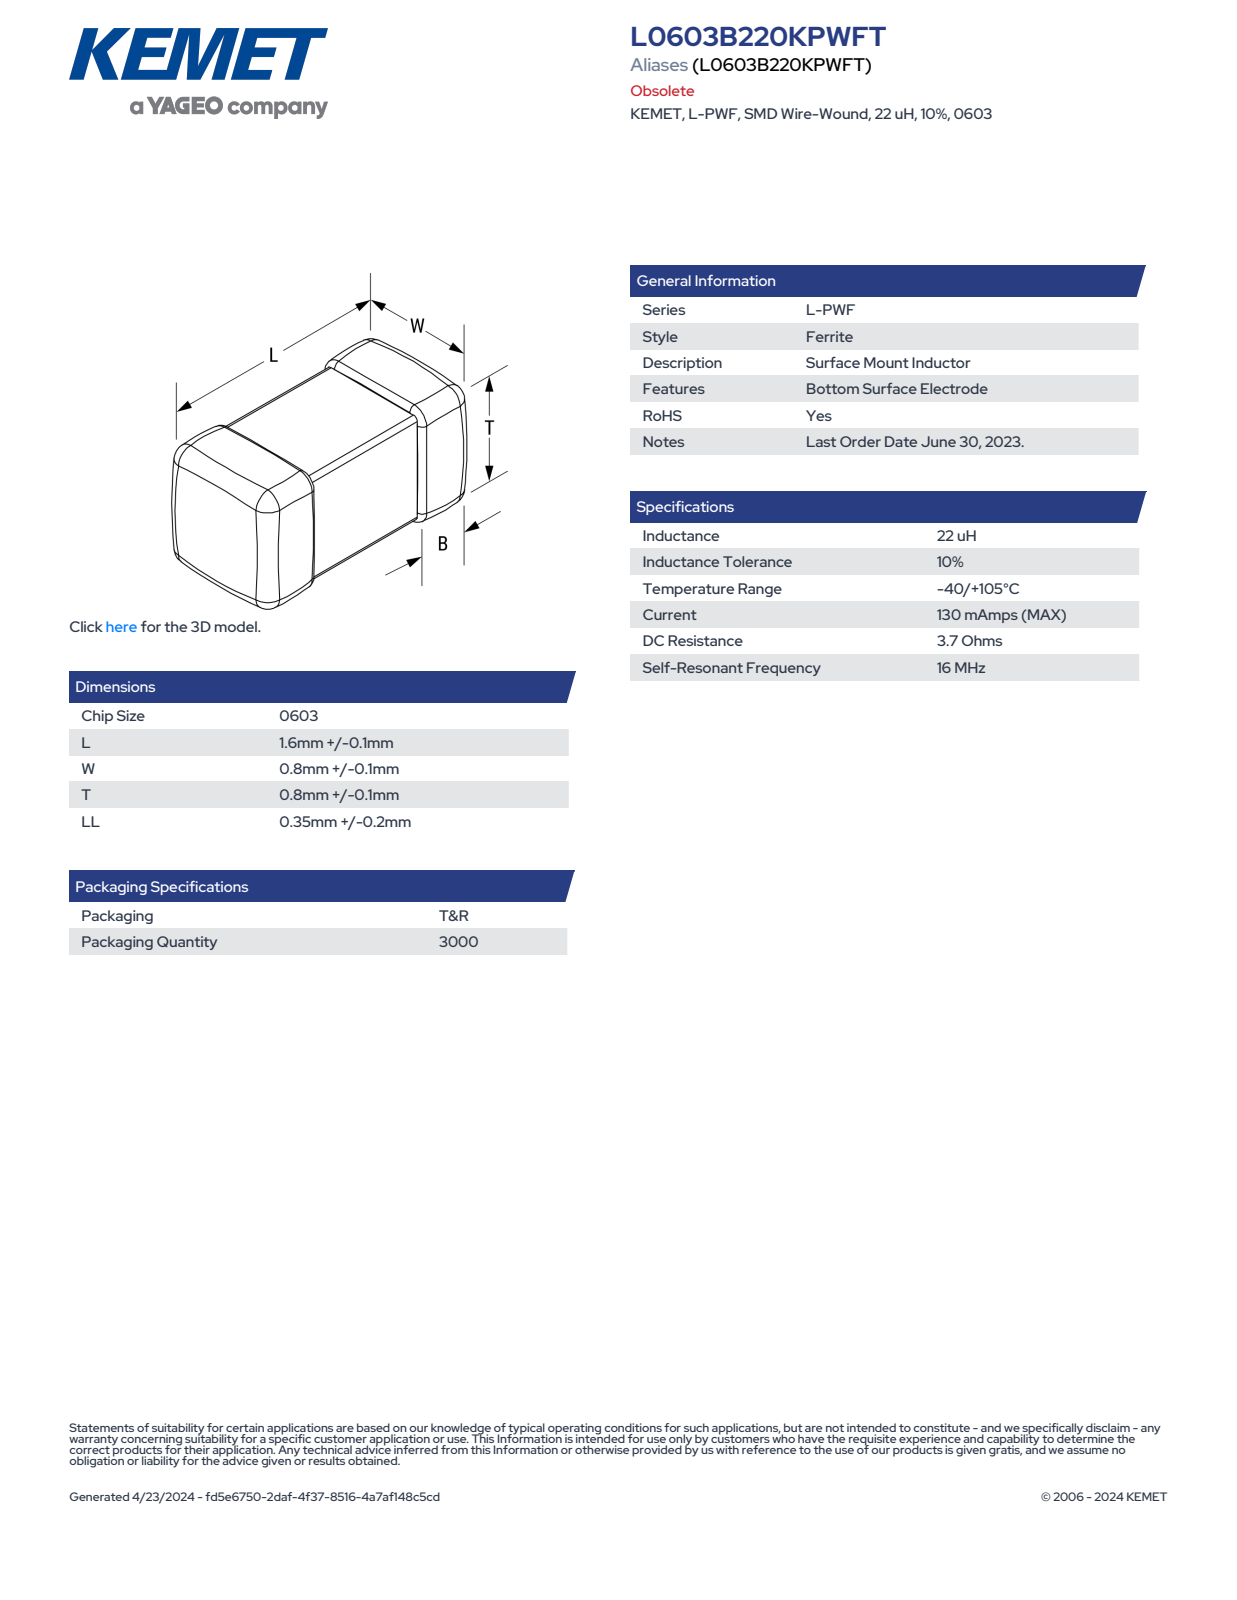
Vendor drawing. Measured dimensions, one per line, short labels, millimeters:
name: IS_KC_0603_L1.7W0.9T0.9LL0.55
written by: SolidWorks 2014 (AUTOMOTIVE_DESIGN)
unit: mm
bodies: 4 solids, 73 faces (73 planar, 0 cylindrical, 0 other)
size: 1.7 × 0.9 × 0.9
volume: 1 mm³; area: 8 mm²
face distances: 0.88, 0.9, 0.86, 1.7, 0.55, 1.15, 0.6, 0.87, 0.89, 0.35
